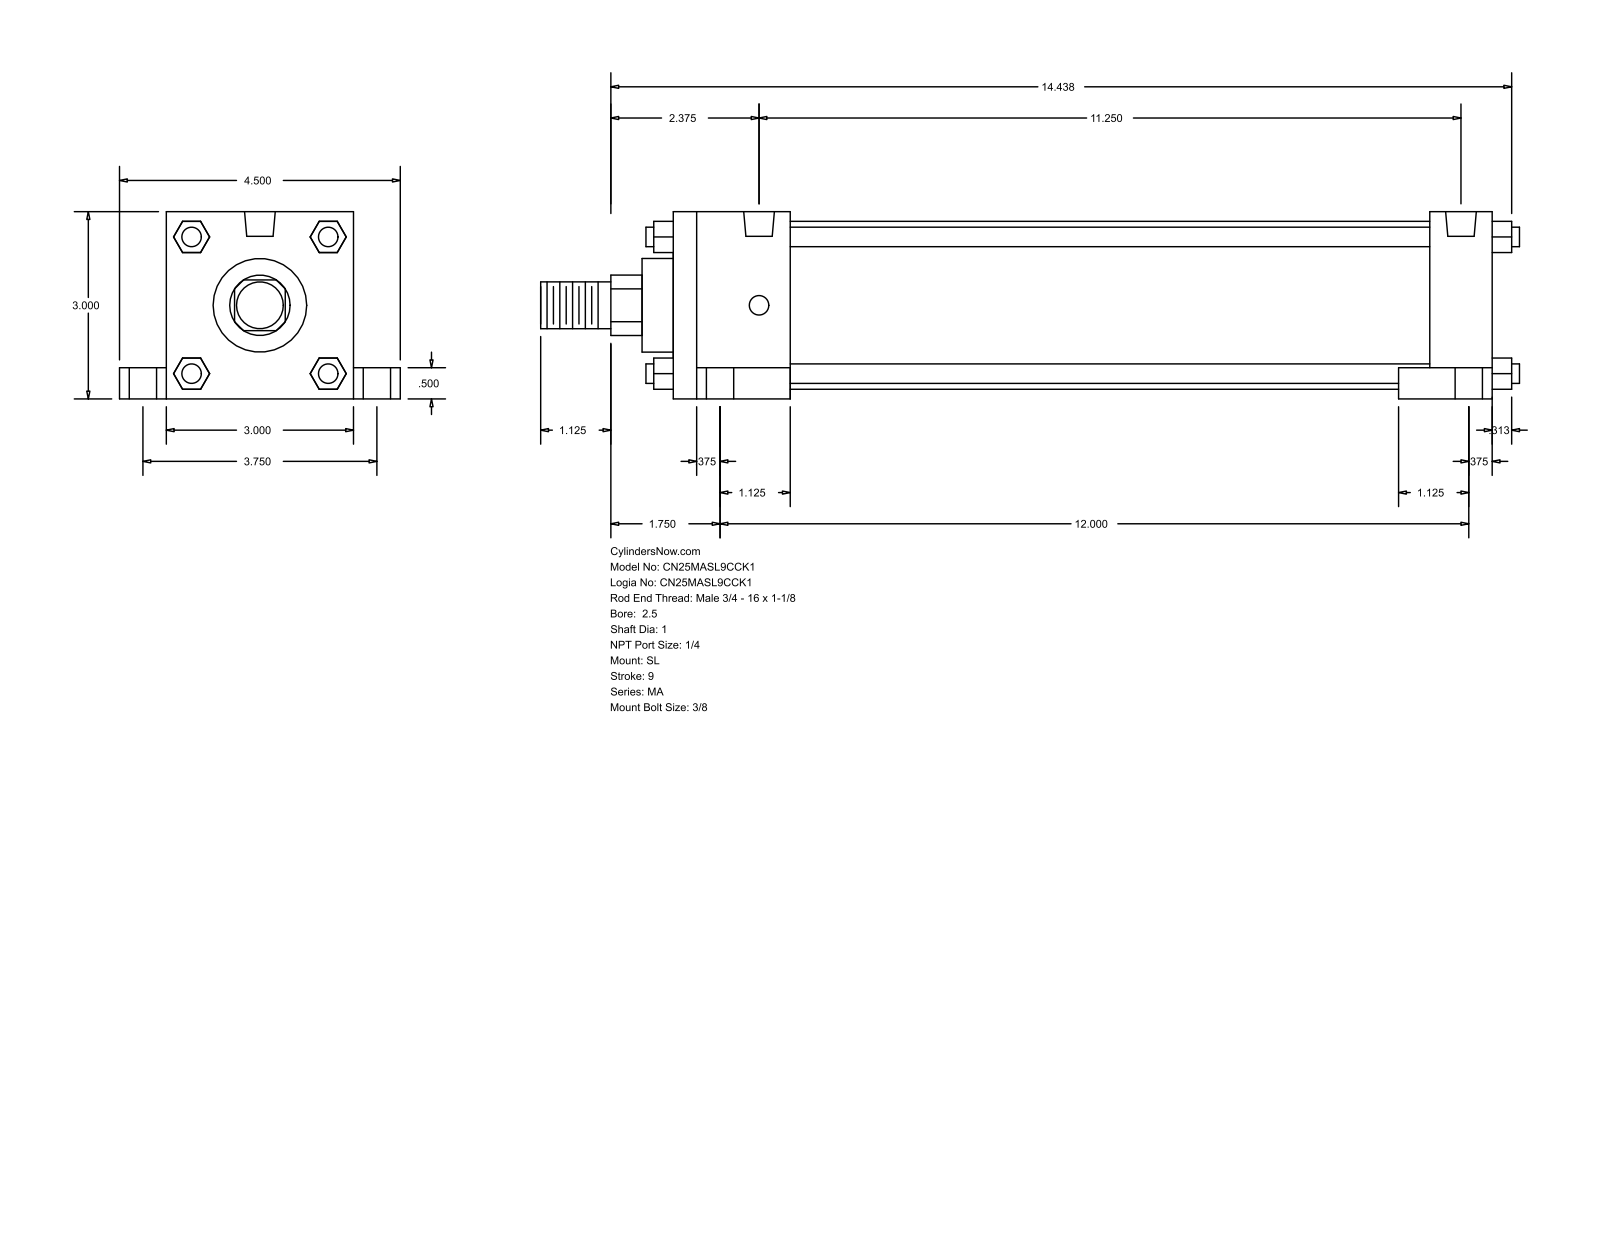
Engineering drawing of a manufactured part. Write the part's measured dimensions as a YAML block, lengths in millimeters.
part_name: "MA_SL__0250_1"
step_written_by: "GSSL Pune (CONFIG_CONTROL_DESIGN)"
units: millimeters
bodies: {solids: 0, faces: 148, planar: 112, cylindrical: 36, other: 0}
overall_size: [398.46, 114.3, 76.2]
round_holes:
  - {diameter: 7.94, count: 4}
  - {diameter: 11.11, count: 4}
  - {diameter: 17.46, count: 4}
  - {diameter: 12.49, count: 2}
round_bosses_or_shafts:
  - {diameter: 7.94, count: 4}
  - {diameter: 68.33, count: 1}
  - {diameter: 38.1, count: 1}
  - {diameter: 25.4, count: 1}
  - {diameter: 19.05, count: 1}
partial_cylinders:
  - {radius: 12.29, count: 1}
face_to_face_distances: [76.2, 333.37, 12.7, 260.35, 25.39, 47.63, 285.74, 307.98, 19.05, 95.25]
hole_center_spacings: [47.73, 50.2, 95.24, 285.74, 292.82, 304.8, 305.36, 319.33]
